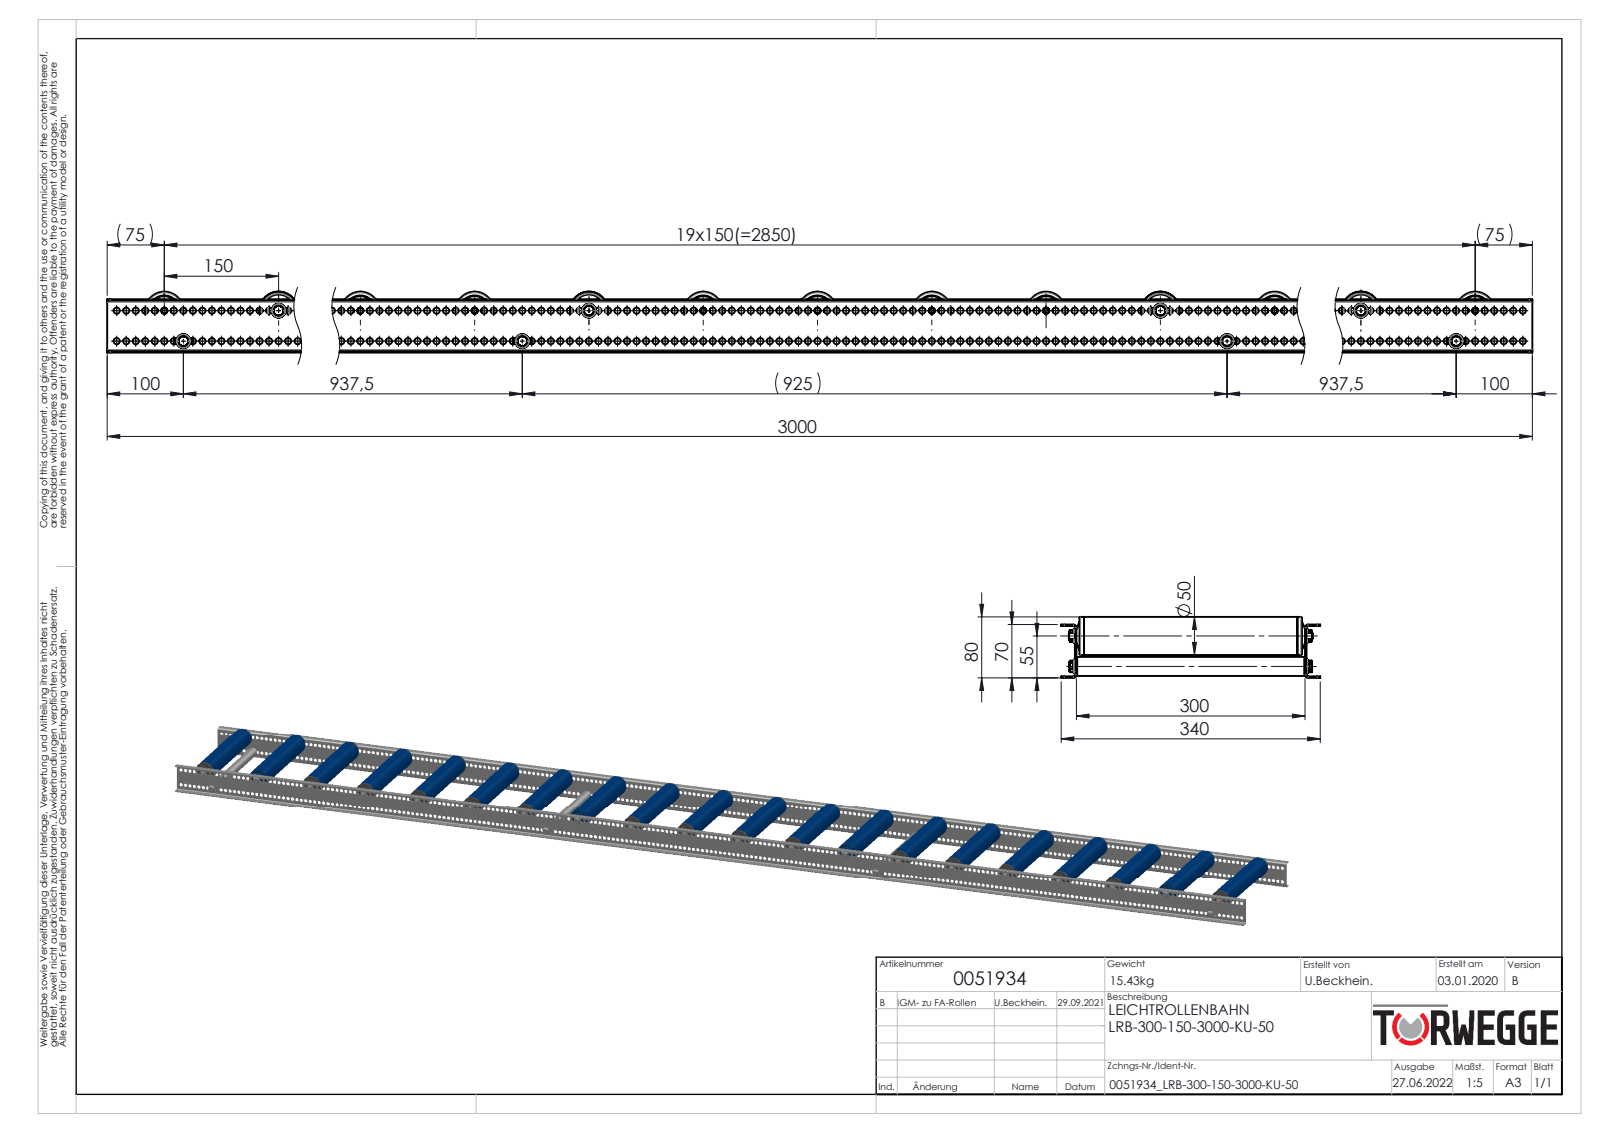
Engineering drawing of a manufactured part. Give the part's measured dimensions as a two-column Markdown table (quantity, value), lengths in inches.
| quantity | value |
| --- | --- |
| part name | KUT100-50x2,8-KB-A12-IGM8-EL=KFG_S100913_KUT100-50x2,8-KB-A12-IGM8-EL=300; 0039780-Achse-ST-Ø12-KFG_IGM8-AL=300; KUT100-50x2,8-KB-A8-FA_KFG_0034513_KUT100-50x2,8-KB-A8-FA-EL=300; 0017015_Tragrollenrohr-Ø50x2,8KU_KFG_0017015_L=280 (+8 more) |
| STEP written by | SolidWorks 2020 (AUTOMOTIVE_DESIGN) |
| units | inches |
| bodies | 414 solids, 8500 faces (2012 planar, 3960 cylindrical, 2528 other) |
| overall size | 118.11 × 13.386 × 3.15 |
| volume | 314 in³ |
| surface area | 6 349 in² |
| round holes (diameter × count) | 0.323 × 478, 0.299 × 16, 0.315 × 16, 0.984 × 16, 1.181 × 16, 1.378 × 16, 1.551 × 16, 1.575 × 16, 0.268 × 8, 0.472 × 4, 0.476 × 4, 0.63 × 4 |
| round bosses / shafts (diameter × count) | 1.969 × 20, 1.748 × 16, 1.496 × 16, 1.417 × 16, 1.299 × 16, 0.866 × 16, 0.827 × 16, 0.984 × 8 |
| partial cylindrical surfaces (radius × count) | 0.024 × 32, 0.03 × 32, 0.096 × 32, 0.098 × 16, 0.192 × 16, 0.276 × 16, 0.157 × 8, 0.079 × 4 |
| main face-to-face distances | 0.079, 11.89, 2.677, 11.811, 11.969, 2.756, 2.598, 0.236, 11.496, 0.472 |
| hole center spacings | 0.492, 0.984, 1.476, 1.969, 2.461, 2.953, 3.445, 3.937 |
